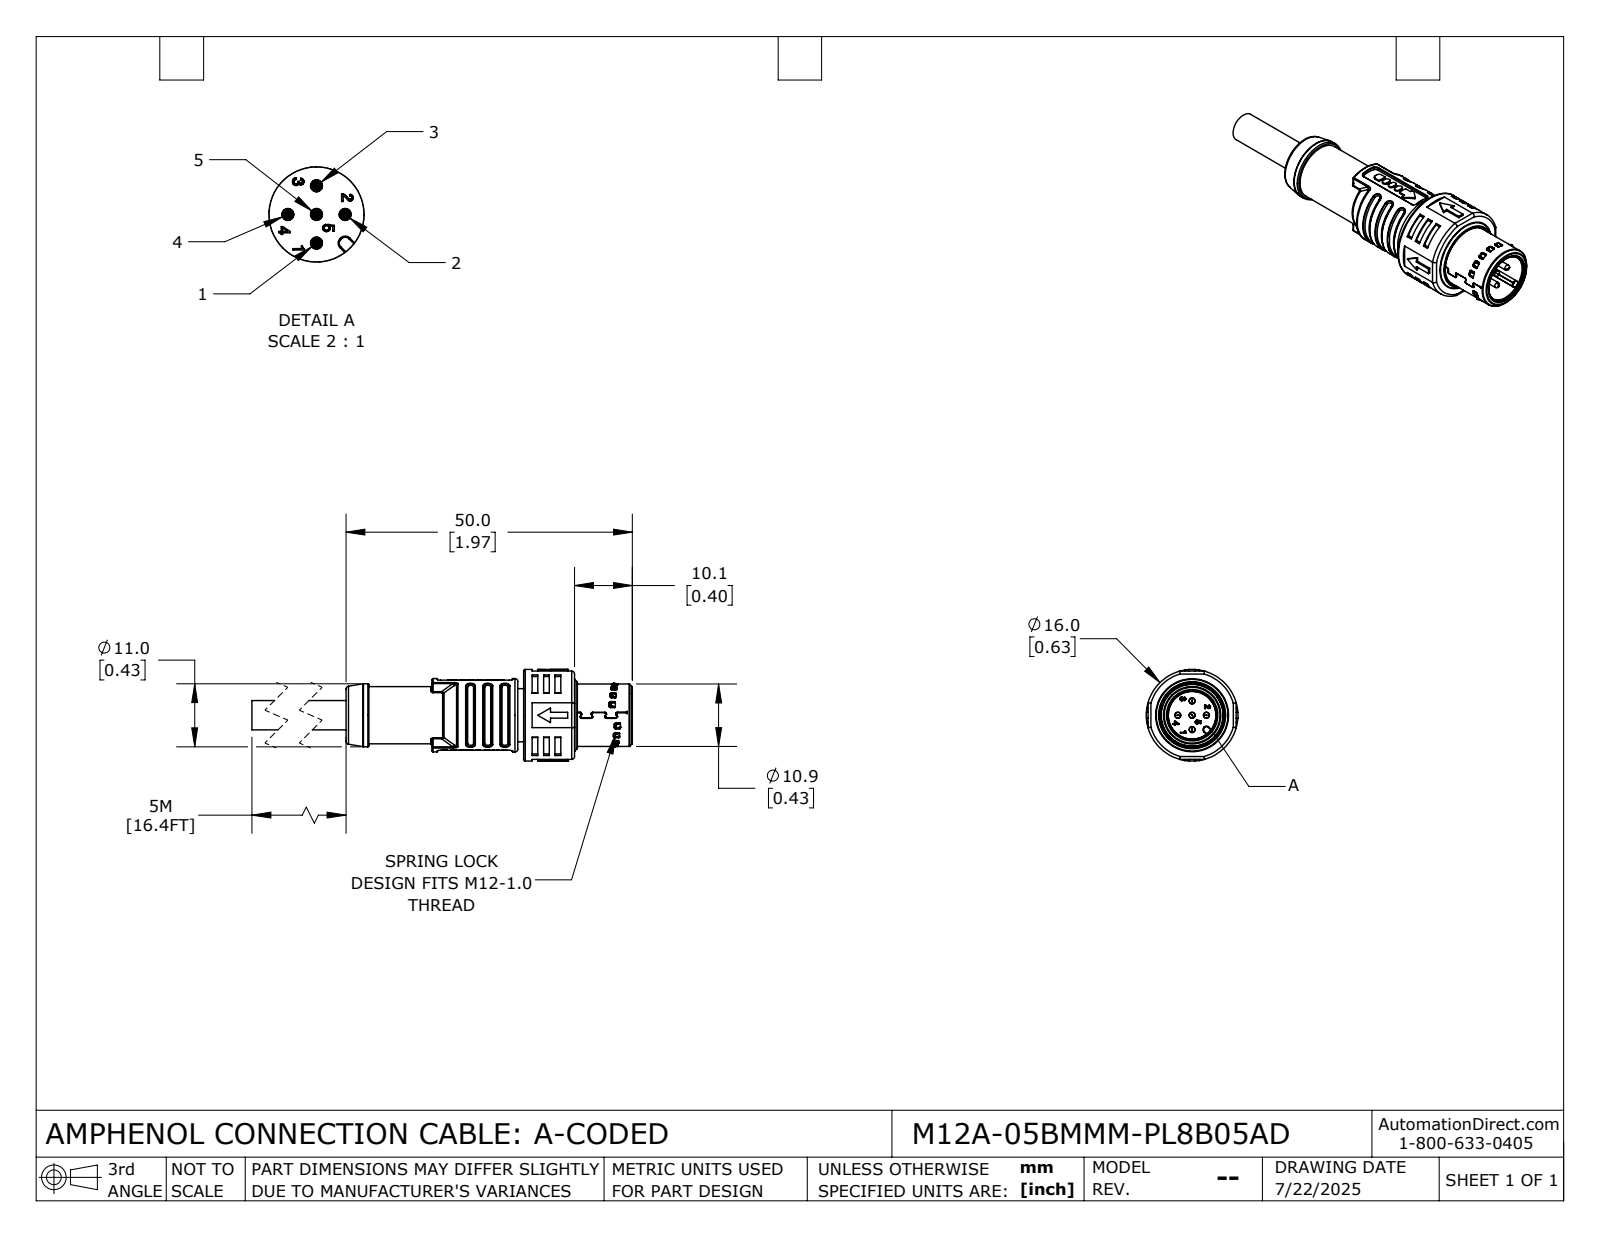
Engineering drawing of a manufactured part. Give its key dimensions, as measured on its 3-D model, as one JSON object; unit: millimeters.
{"part_name": "M12A-05BMMM-PL8B05AD", "step_written_by": "SolidWorks 2024 (CONFIG_CONTROL_DESIGN)", "units": "millimeters", "bodies": {"solids": 1, "faces": 2230, "planar": 1085, "cylindrical": 648, "other": 497}, "overall_size": [65, 16, 16], "volume_mm3": 5076, "surface_area_mm2": 5586, "round_holes": [[1.05, 5], [8.3, 1], [9, 1], [10.15, 1], [10.5, 1], [10.9, 1], [11.5, 1], [11.8, 1], [14.2, 1]], "round_bosses_or_shafts": [[1, 5], [16, 1], [14.1, 1], [12.8, 1], [12.4, 1], [11, 1], [10.45, 1], [10.4, 1]], "partial_cylinders_radius": [[0.2, 114], [0.25, 66], [0.3, 64], [0.15, 44], [0.5, 38], [0.13, 12], [0.7, 11], [0.1, 10]], "face_to_face_distances": [1, 10.1, 8.9, 8.6, 2.5, 30, 1.5, 1.2, 32.5, 15.4], "hole_center_spacings": [2.5, 3.54, 5]}
